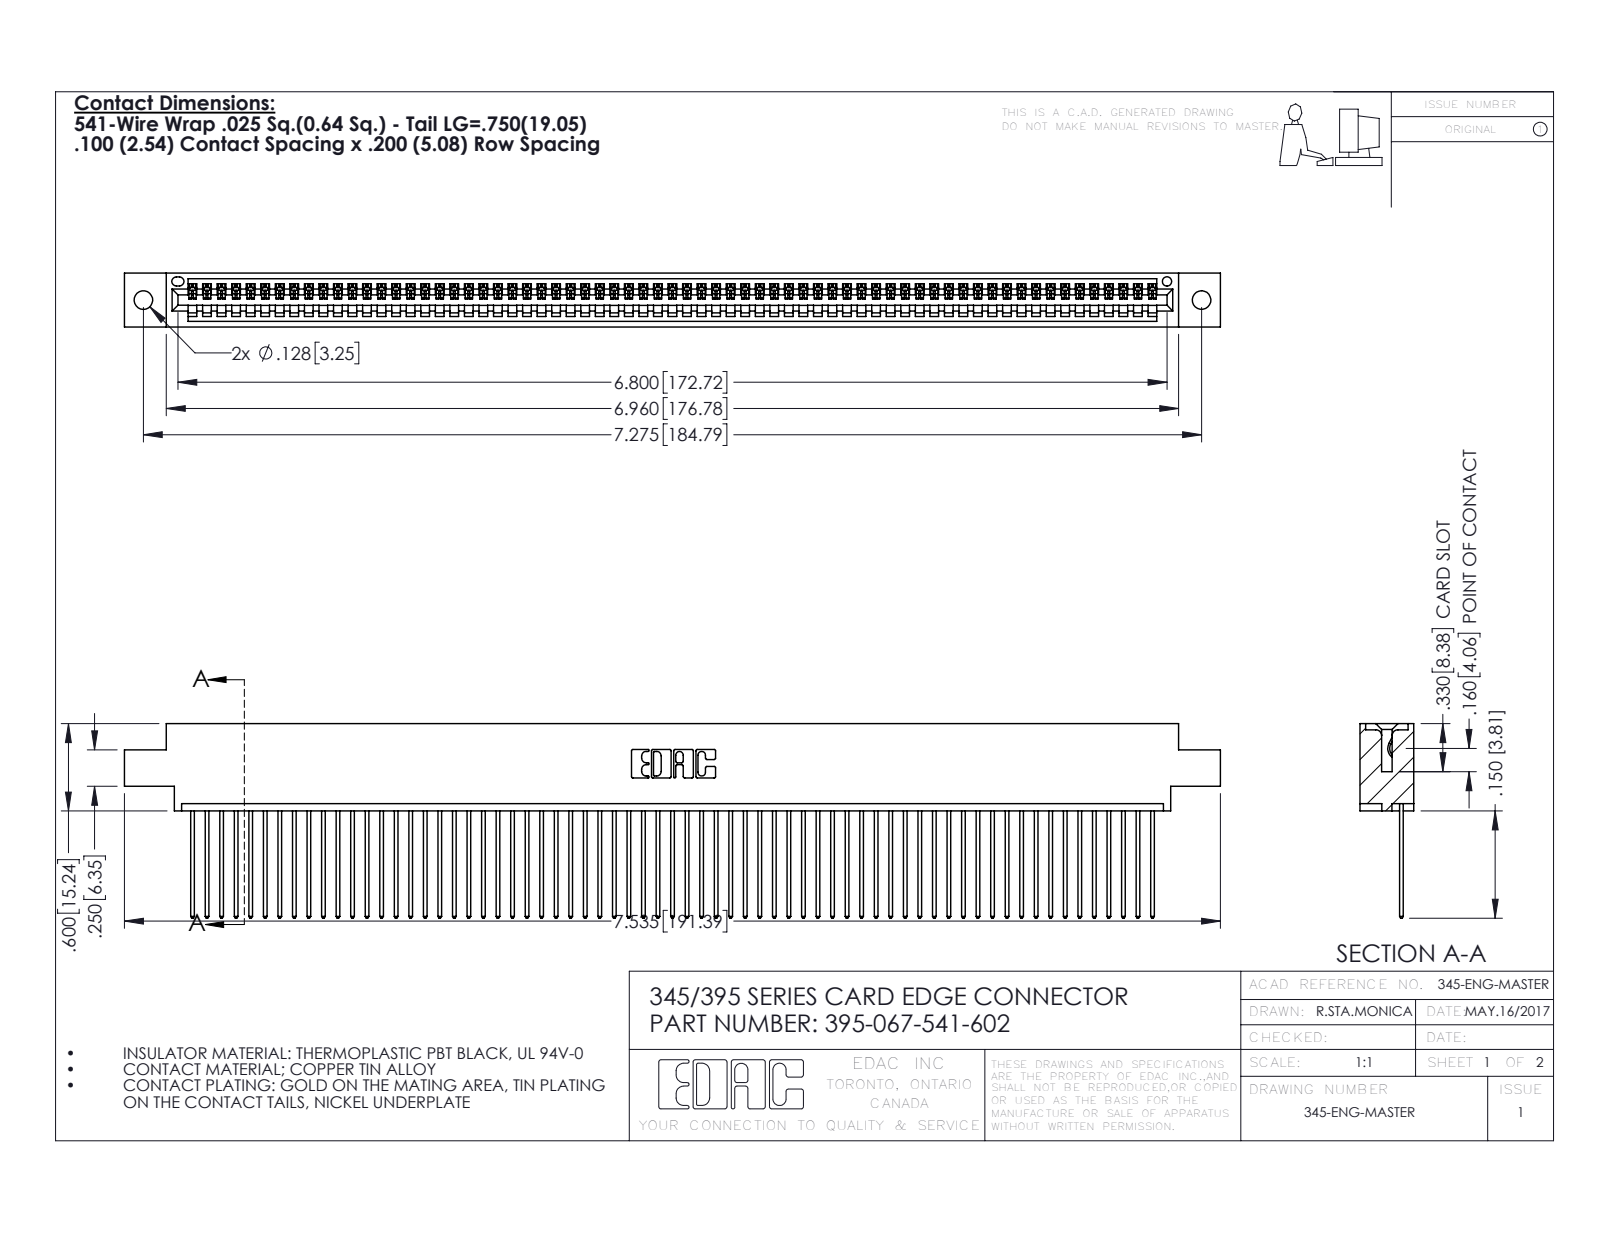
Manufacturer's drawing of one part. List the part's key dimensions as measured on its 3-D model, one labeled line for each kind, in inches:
Part name (STEP PRODUCT): 345 Part_0.170 Offset - 0.128 Dia; 345-292-001_345-293-141; 395-067-541-602
STEP written by: SolidWorks 2016 (CONFIG_CONTROL_DESIGN)
Units: inches
Bodies: 68 solids, 4016 faces (2764 planar, 1252 cylindrical, 0 other)
Overall size (bounding box): 7.535 × 1.337 × 0.37
Volume: 1.126 in³ · Surface area: 40.33 in²
Round holes (diameter × count): ⌀0.128 ×2, ⌀0.064 ×1
Partial cylindrical surfaces — rounded edges, fillets, slot ends (radius × count): R0.006 ×134, R0.01 ×134, R0.01 ×22, R0.007 ×6, R0.031 ×6, R0.026 ×3, R0.031 ×2, R0.04 ×2
Main face-to-face distances: 0.072, 0.298, 0.098, 0.272, 0.025, 0.37, 0.2, 0.225, 0.175, 0.149
Hole centre spacings: 0.27, 7.039, 7.275
